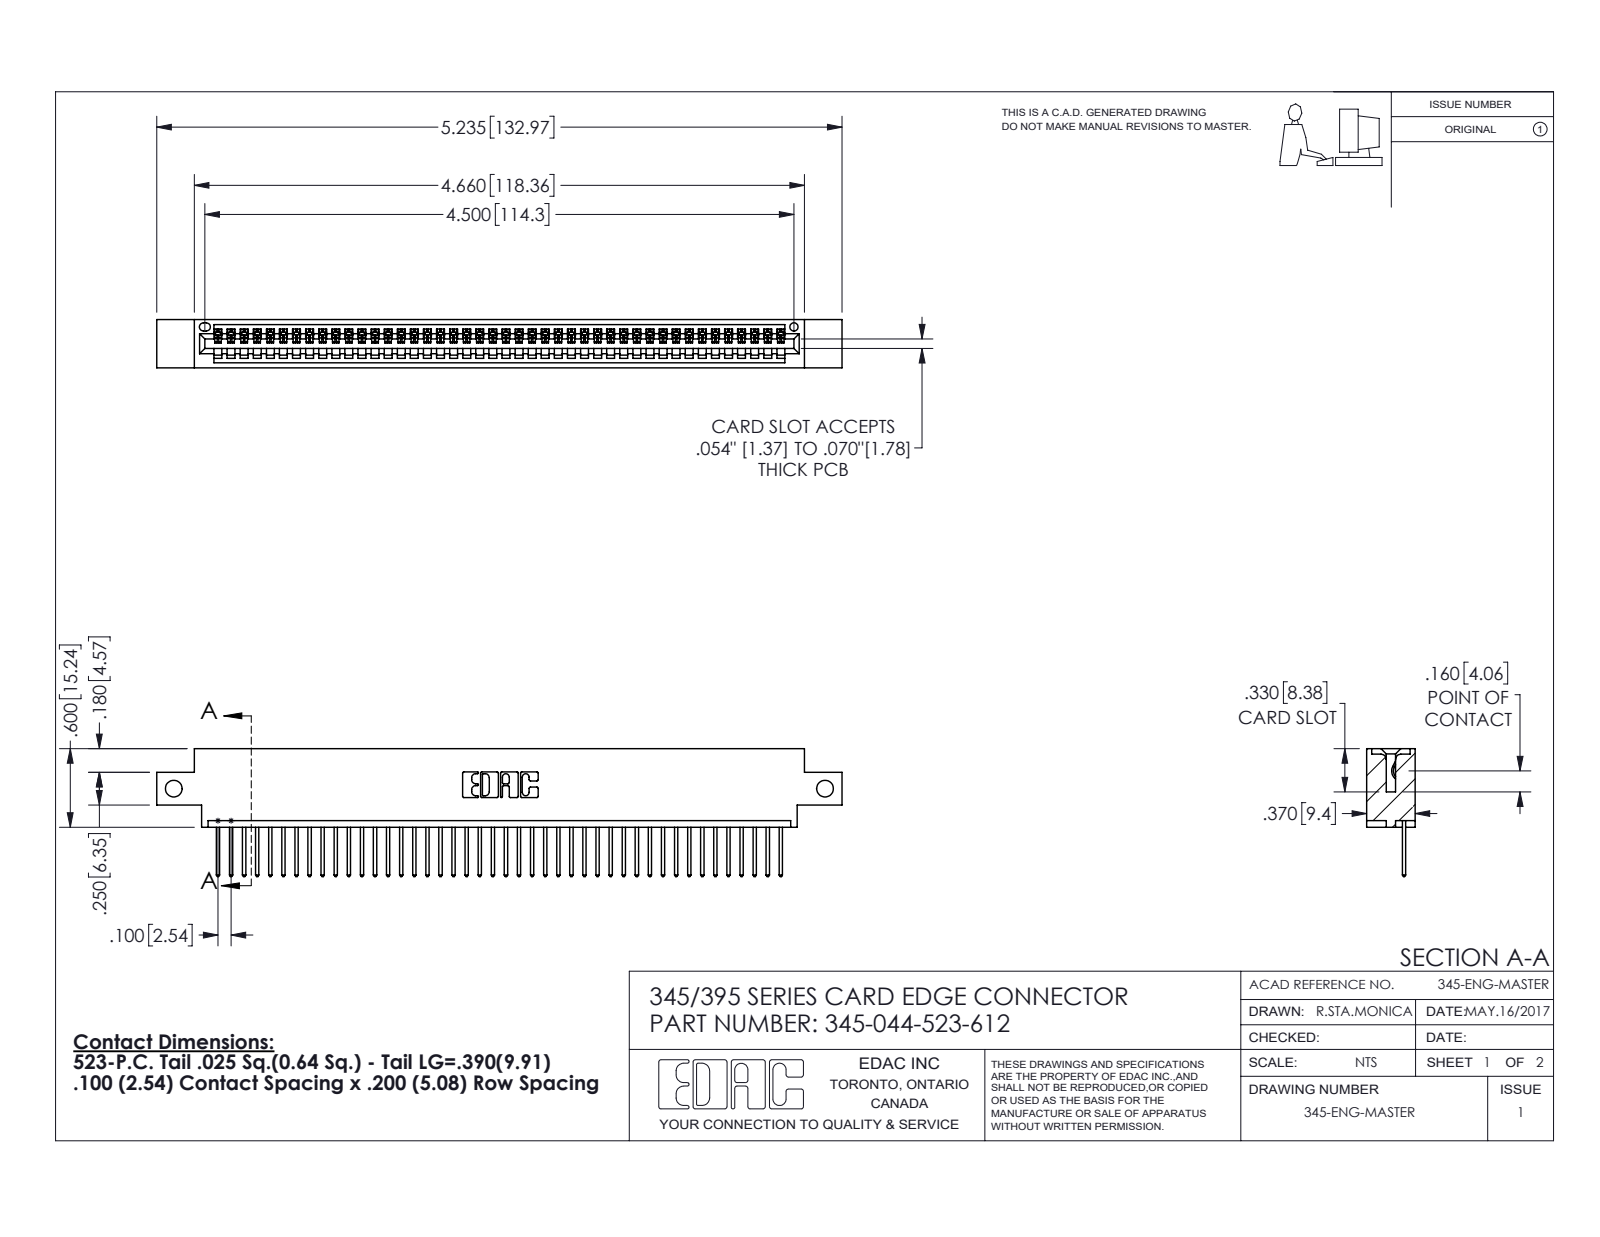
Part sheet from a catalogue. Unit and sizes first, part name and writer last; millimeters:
Units: millimetres
Overall size (bounding box): 133 × 24.8 × 9.4
Round holes (diameter × count): ⌀3.3 ×2, ⌀1.6 ×1
Partial cylindrical surfaces — rounded edges, fillets, slot ends (radius × count): R0.2 ×88, R0.3 ×88, R0.3 ×22, R0.2 ×6, R0.8 ×6, R0.7 ×3, R0.8 ×2, R1 ×2
Main face-to-face distances: 7.6, 1.8, 9.4, 5.1, 2.5, 6.9, 0.6, 5.7, 4.4, 3.8
Hole centre spacings: 126.4
Volume: 12 400 mm³ · Surface area: 16 570 mm²
Bodies: 45 solids, 2682 faces (1844 planar, 838 cylindrical, 0 other)
Part name (STEP PRODUCT): 345 Part_0.170 Offset - Side Mount; 345-044-523-612; 345-292-001_345-293-123
STEP written by: SolidWorks 2016 (CONFIG_CONTROL_DESIGN)
